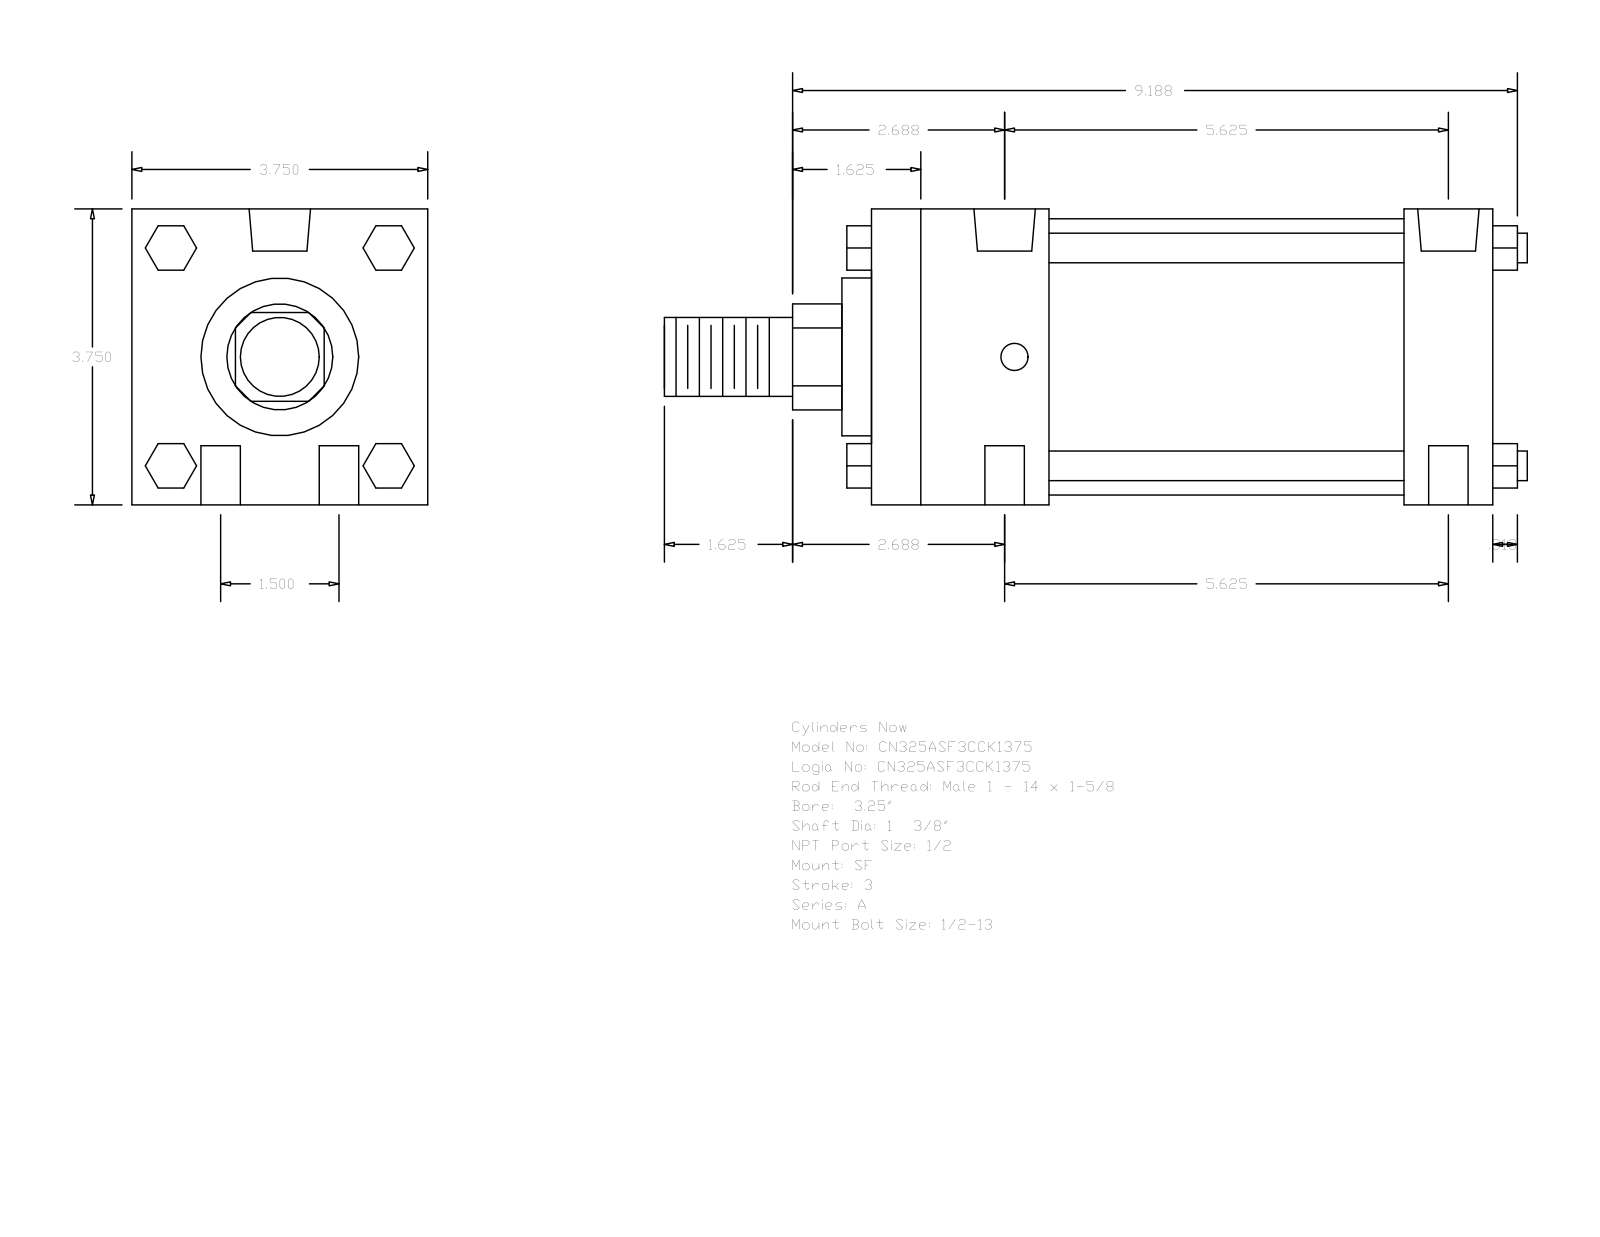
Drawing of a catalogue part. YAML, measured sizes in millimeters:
part_name: "A_SF__0325_1.375"
step_written_by: "GSSL Pune (CONFIG_CONTROL_DESIGN)"
units: millimeters
bodies: {solids: 0, faces: 124, planar: 94, cylindrical: 30, other: 0}
overall_size: [277.81, 95.25, 95.25]
round_holes:
  - {diameter: 12.7, count: 4}
  - {diameter: 8.73, count: 2}
  - {diameter: 19.77, count: 2}
round_bosses_or_shafts:
  - {diameter: 9.53, count: 4}
  - {diameter: 88.9, count: 1}
  - {diameter: 50.8, count: 1}
  - {diameter: 34.92, count: 1}
  - {diameter: 25.4, count: 1}
partial_cylinders:
  - {radius: 17.06, count: 1}
face_to_face_distances: [95.24, 200.03, 57.15, 28.58, 171.45, 114.3, 142.88, 66.67, 9.52, 180.97]
hole_center_spacings: [19.05, 144.14, 142.88, 38.1, 147.87, 136.52]
